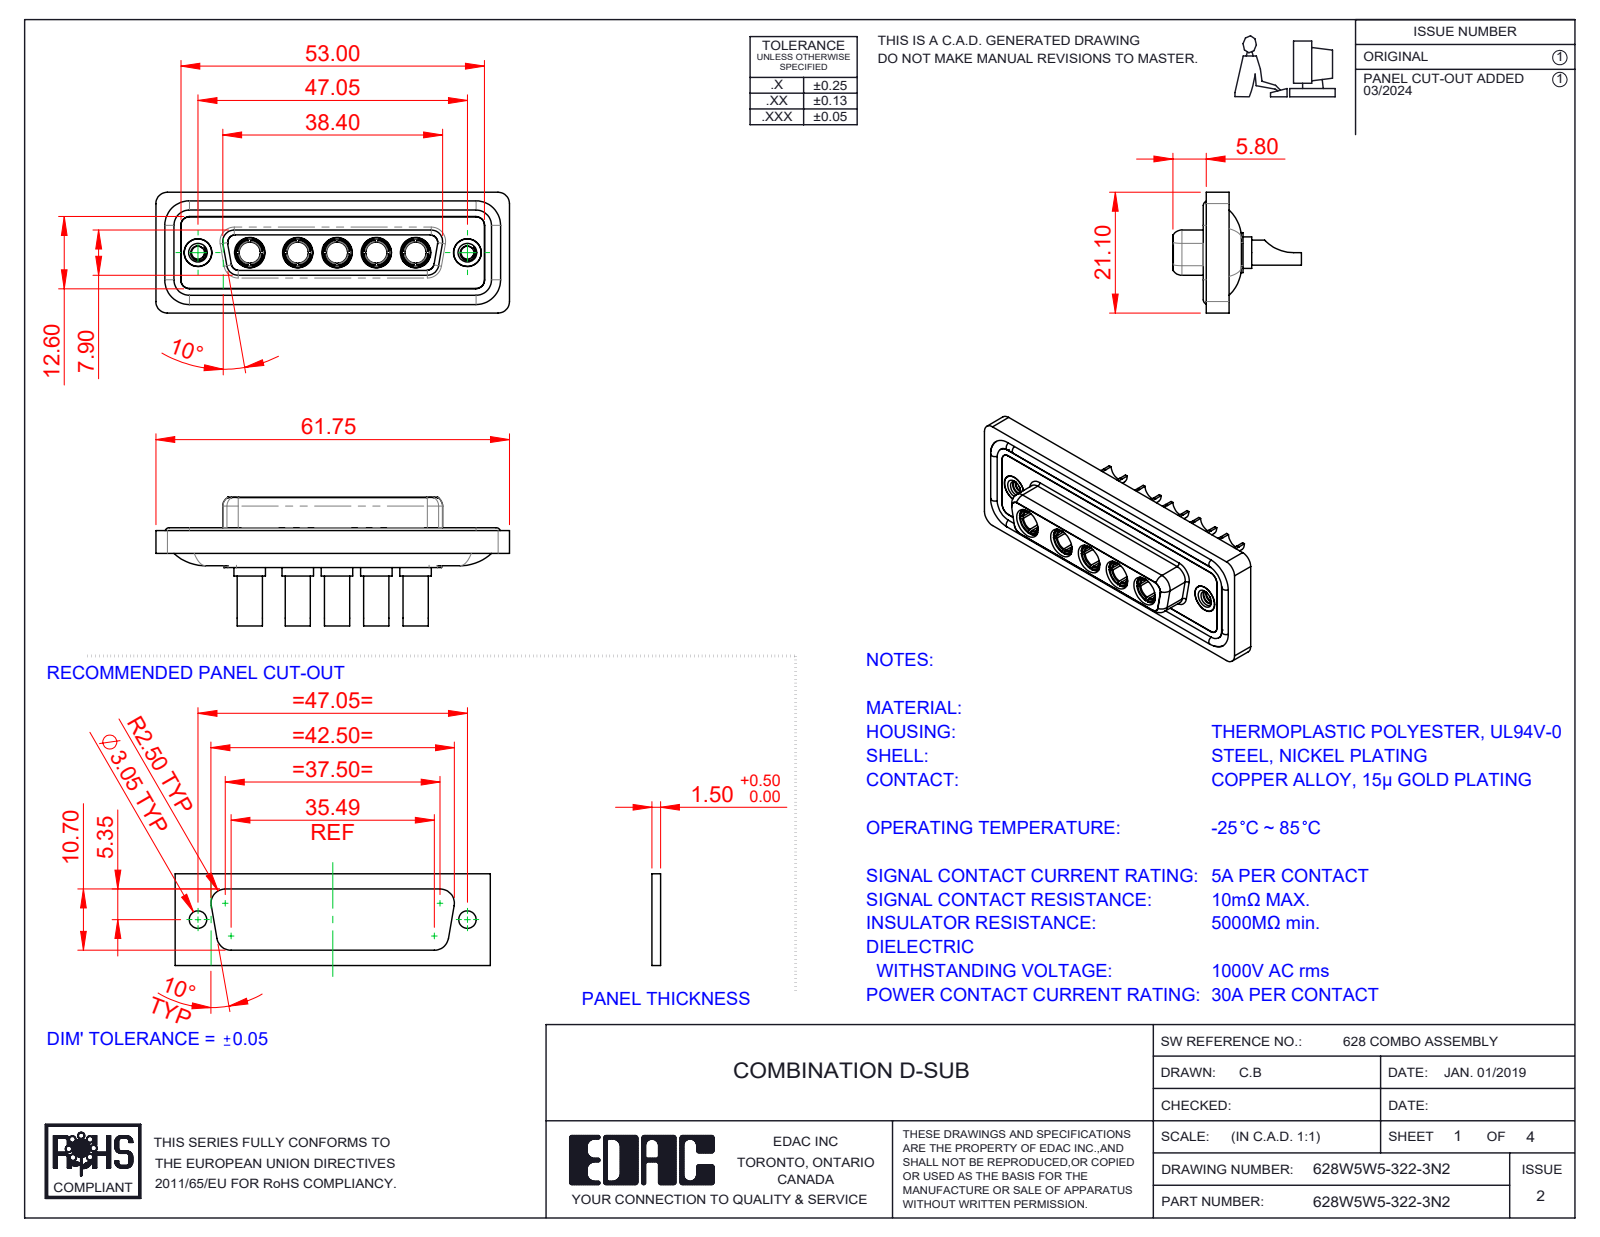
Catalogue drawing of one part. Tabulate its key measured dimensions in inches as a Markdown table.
| quantity | value |
| --- | --- |
| part name | Power Socket_30A SC; 628W5W5-322-3N2; 628Combo Shell Front_25 Contacts; 628Combo Housing_5W5 (+3 more) |
| STEP written by | SolidWorks 2023 (CONFIG_CONTROL_DESIGN) |
| units | inches |
| bodies | 17 solids, 786 faces (265 planar, 318 cylindrical, 203 other) |
| overall size | 2.431 × 0.884 × 0.831 |
| volume | 0.506 in³ |
| surface area | 21.63 in² |
| round holes (diameter × count) | 0.191 × 7, 0.138 × 5, 0.146 × 5, 0.209 × 5, 0.089 × 2, 0.157 × 2, 0.159 × 2, 0.197 × 2 |
| round bosses / shafts (diameter × count) | 0.217 × 5, 0.205 × 5, 0.195 × 5, 0.187 × 5, 0.173 × 5, 0.148 × 5, 0.063 × 4, 0.195 × 2 |
| partial cylindrical surfaces (radius × count) | 0.059 × 22, 0.079 × 18, 0.053 × 8, 0.063 × 8, 0.083 × 5, 0.01 × 4, 0.02 × 4, 0.024 × 4 |
| main face-to-face distances | 0.016, 0.071, 0.293, 0.222, 0.02, 0.278, 0.26, 0.063, 0.043, 0.114 |
| hole center spacings | 0.27, 0.356, 0.54, 1.496, 0.33, 0.6, 0.626, 0.686 |
